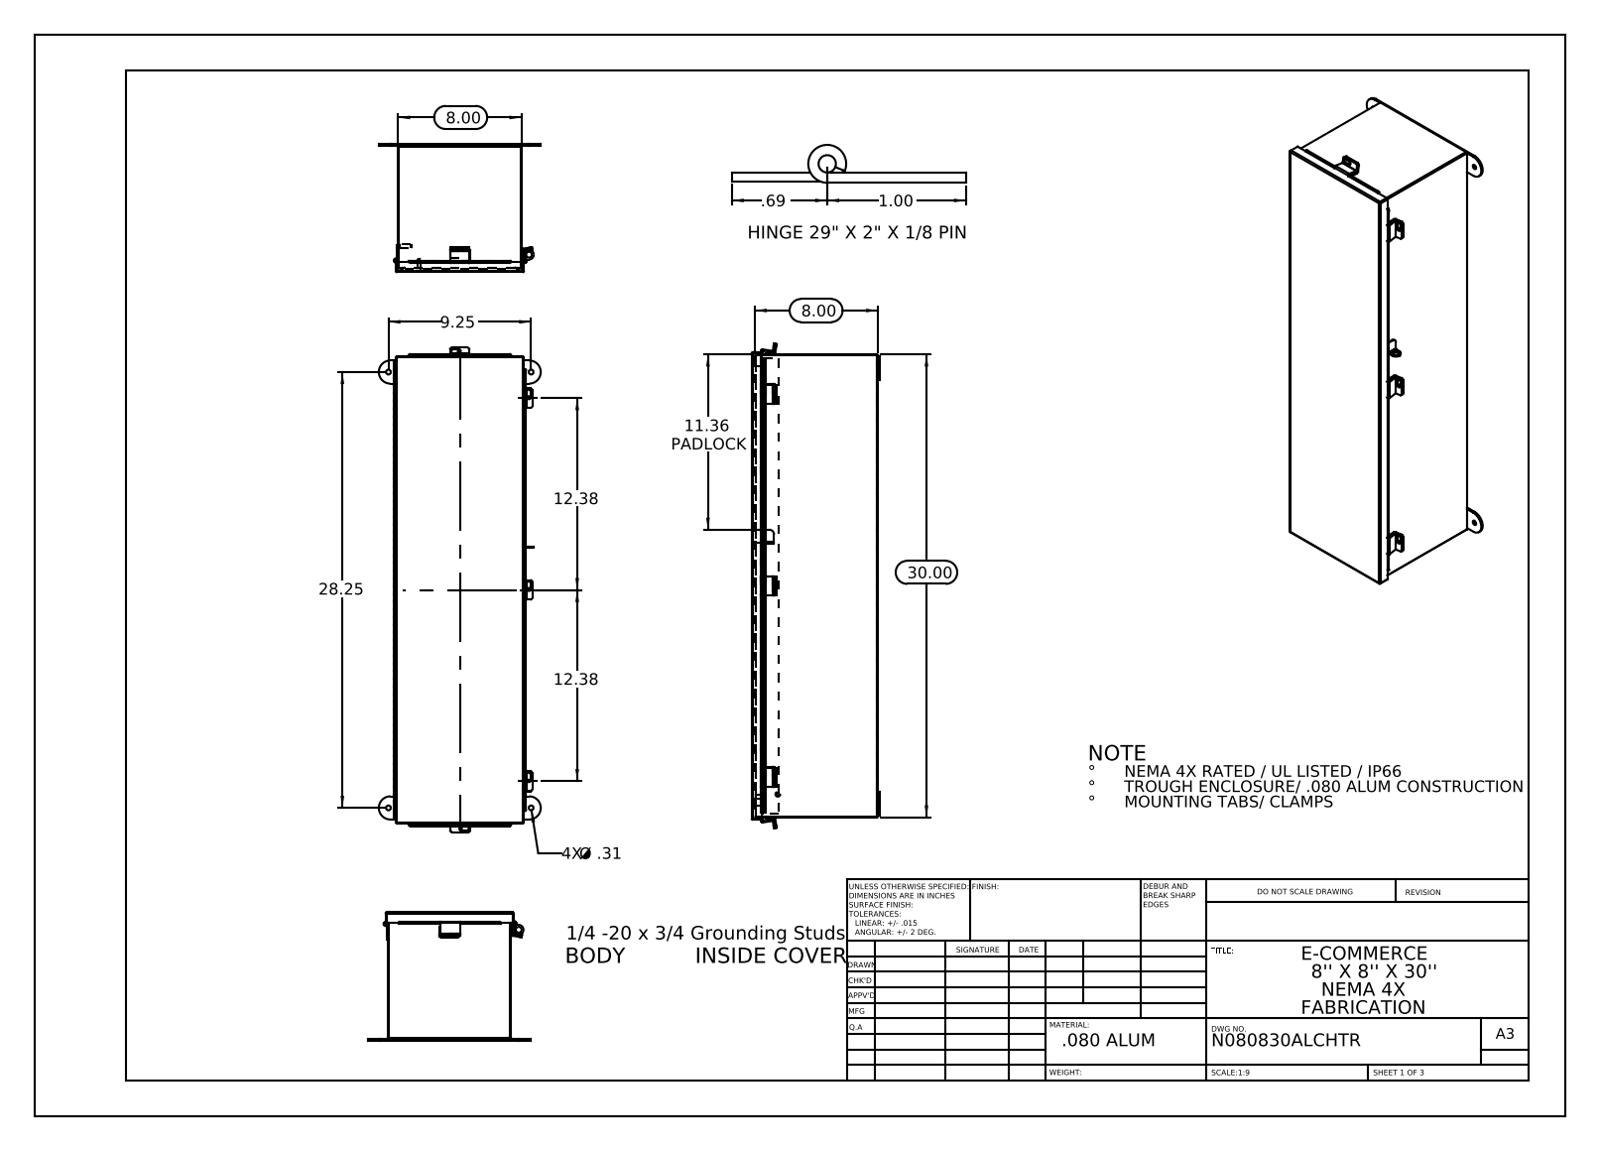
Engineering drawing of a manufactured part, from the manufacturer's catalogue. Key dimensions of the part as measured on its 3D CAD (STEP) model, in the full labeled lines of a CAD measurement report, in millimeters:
Part name (STEP PRODUCT): N080830SSCHTR JIC Top; N080830SSCHTR JIC_Cover_Template; N080830SSCHTR JIC Enclosure Template; N080830SSCHTR JIC Clamp Bracket (+8 more)
STEP written by: SolidWorks 2013 (CONFIG_CONTROL_DESIGN)
Units: millimetres
Bodies: 21 solids, 1006 faces (613 planar, 373 cylindrical, 20 other)
Overall size (bounding box): 797.7 × 266.7 × 211.8
Volume: 1 577 000 mm³ · Surface area: 1 663 000 mm²
Round holes (diameter × count): ⌀6.4 ×5, ⌀8 ×4, ⌀3.2 ×1, ⌀9.5 ×1
Round bosses / shafts (diameter × count): ⌀8 ×2, ⌀6 ×2, ⌀6.9 ×1, ⌀6.4 ×1
Partial cylindrical surfaces — rounded edges, fillets, slot ends (radius × count): R3.2 ×19, R0.2 ×12, R0.3 ×10, R2.2 ×10, R3.4 ×10, R2.1 ×6, R2.5 ×6, R19.1 ×4
Main face-to-face distances: 1.9, 201.3, 206.5, 203.2, 199.4, 208.4, 204.5, 760.1, 3.8, 205.1
Hole centre spacings: 235, 315.6, 717.6, 755, 219.3, 631.2
